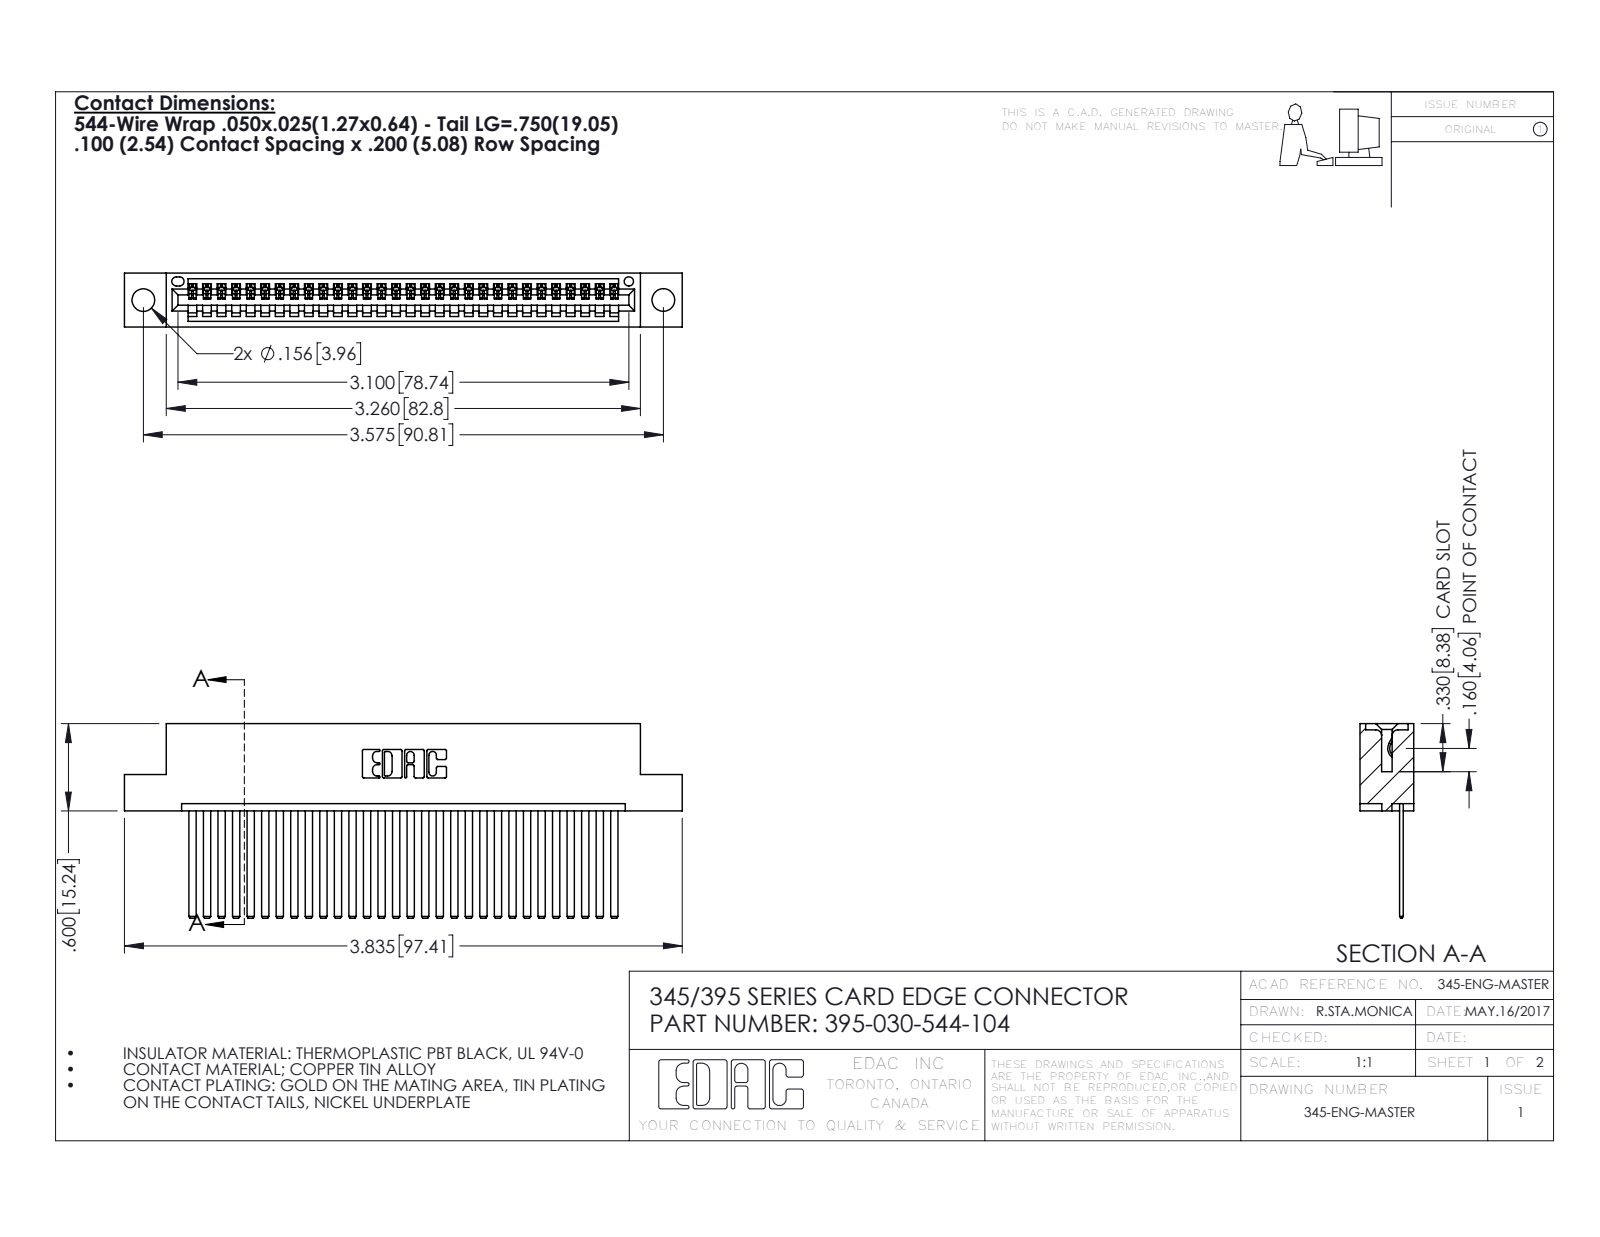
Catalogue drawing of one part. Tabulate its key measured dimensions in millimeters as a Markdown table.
| quantity | value |
| --- | --- |
| part name | 395-030-544-104; 345 Part_Flush Mounting Lugs - 0.156 Dia-TH; 345-292-001_345-293-144 |
| STEP written by | SolidWorks 2016 (CONFIG_CONTROL_DESIGN) |
| units | millimeters |
| bodies | 31 solids, 1686 faces (1160 planar, 526 cylindrical, 0 other) |
| overall size | 97.4 × 34 × 9.4 |
| volume | 9 410 mm³ |
| surface area | 13 200 mm² |
| round holes (diameter × count) | 4 × 2, 1.6 × 1 |
| partial cylindrical surfaces (radius × count) | 0.2 × 60, 0.3 × 22, 0.2 × 6, 0.8 × 6, 0.7 × 3, 0.8 × 2, 1 × 2, 0.4 × 1 |
| main face-to-face distances | 1.8, 7.6, 2.5, 0.6, 6.9, 5.1, 9.4, 5.7, 3.8, 1.8 |
| hole center spacings | 6.9, 84.8, 90.8 |
